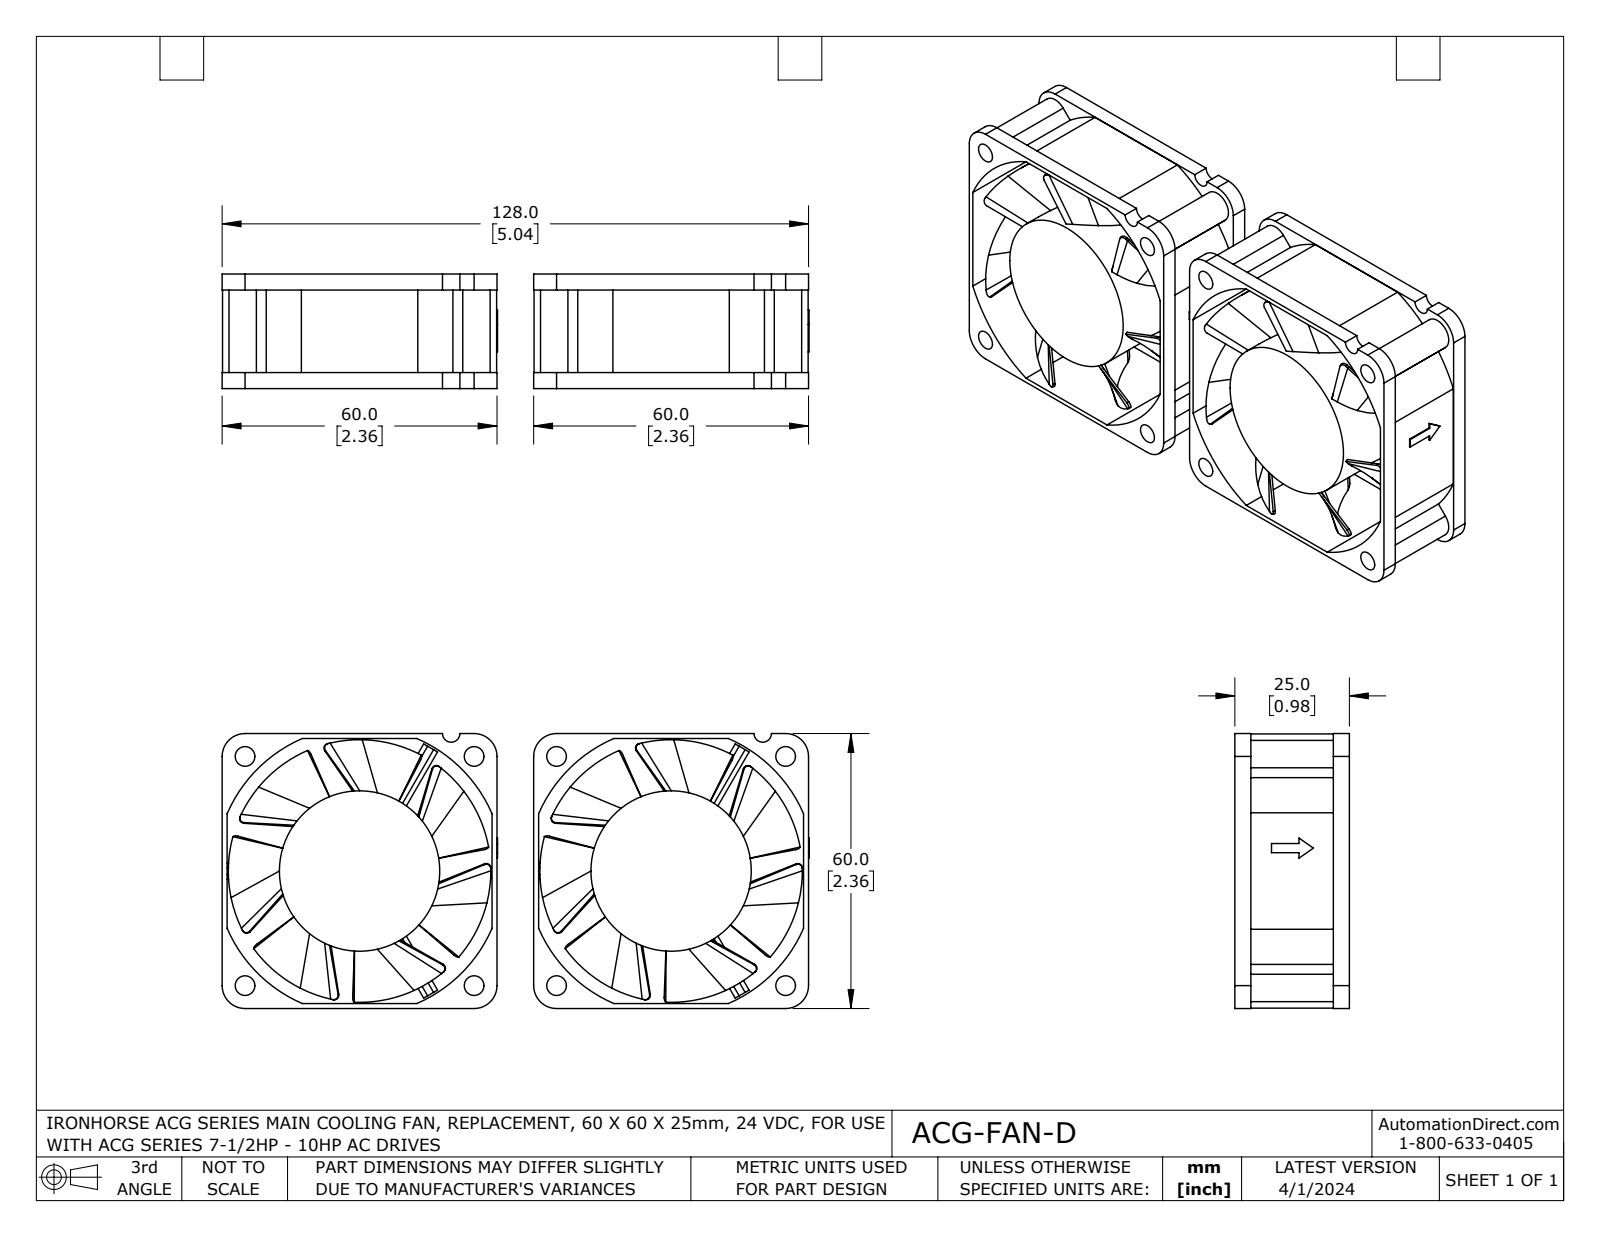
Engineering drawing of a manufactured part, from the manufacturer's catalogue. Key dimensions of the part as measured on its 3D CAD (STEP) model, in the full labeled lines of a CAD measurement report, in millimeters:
Part name (STEP PRODUCT): ACG-FAN-D
STEP written by: SolidWorks 2021 (AUTOMOTIVE_DESIGN)
Units: millimetres
Bodies: 4 solids, 444 faces (118 planar, 116 cylindrical, 210 other)
Overall size (bounding box): 128.1 × 60 × 25
Volume: 31 090 mm³ · Surface area: 55 100 mm²
Round holes (diameter × count): ⌀4.3 ×8, ⌀33 ×2
Round bosses / shafts (diameter × count): ⌀35 ×2
Partial cylindrical surfaces — rounded edges, fillets, slot ends (radius × count): R1 ×20, R3.5 ×8, R5 ×8, R1.9 ×2, R31.5 ×2, R32.5 ×2
Main face-to-face distances: 1, 58.8, 24, 25, 68, 57.8, 3.5, 20.5, 59.8, 21.5
Hole centre spacings: 35.4, 50, 68, 49.7, 70.7, 84.4, 96.3, 18
